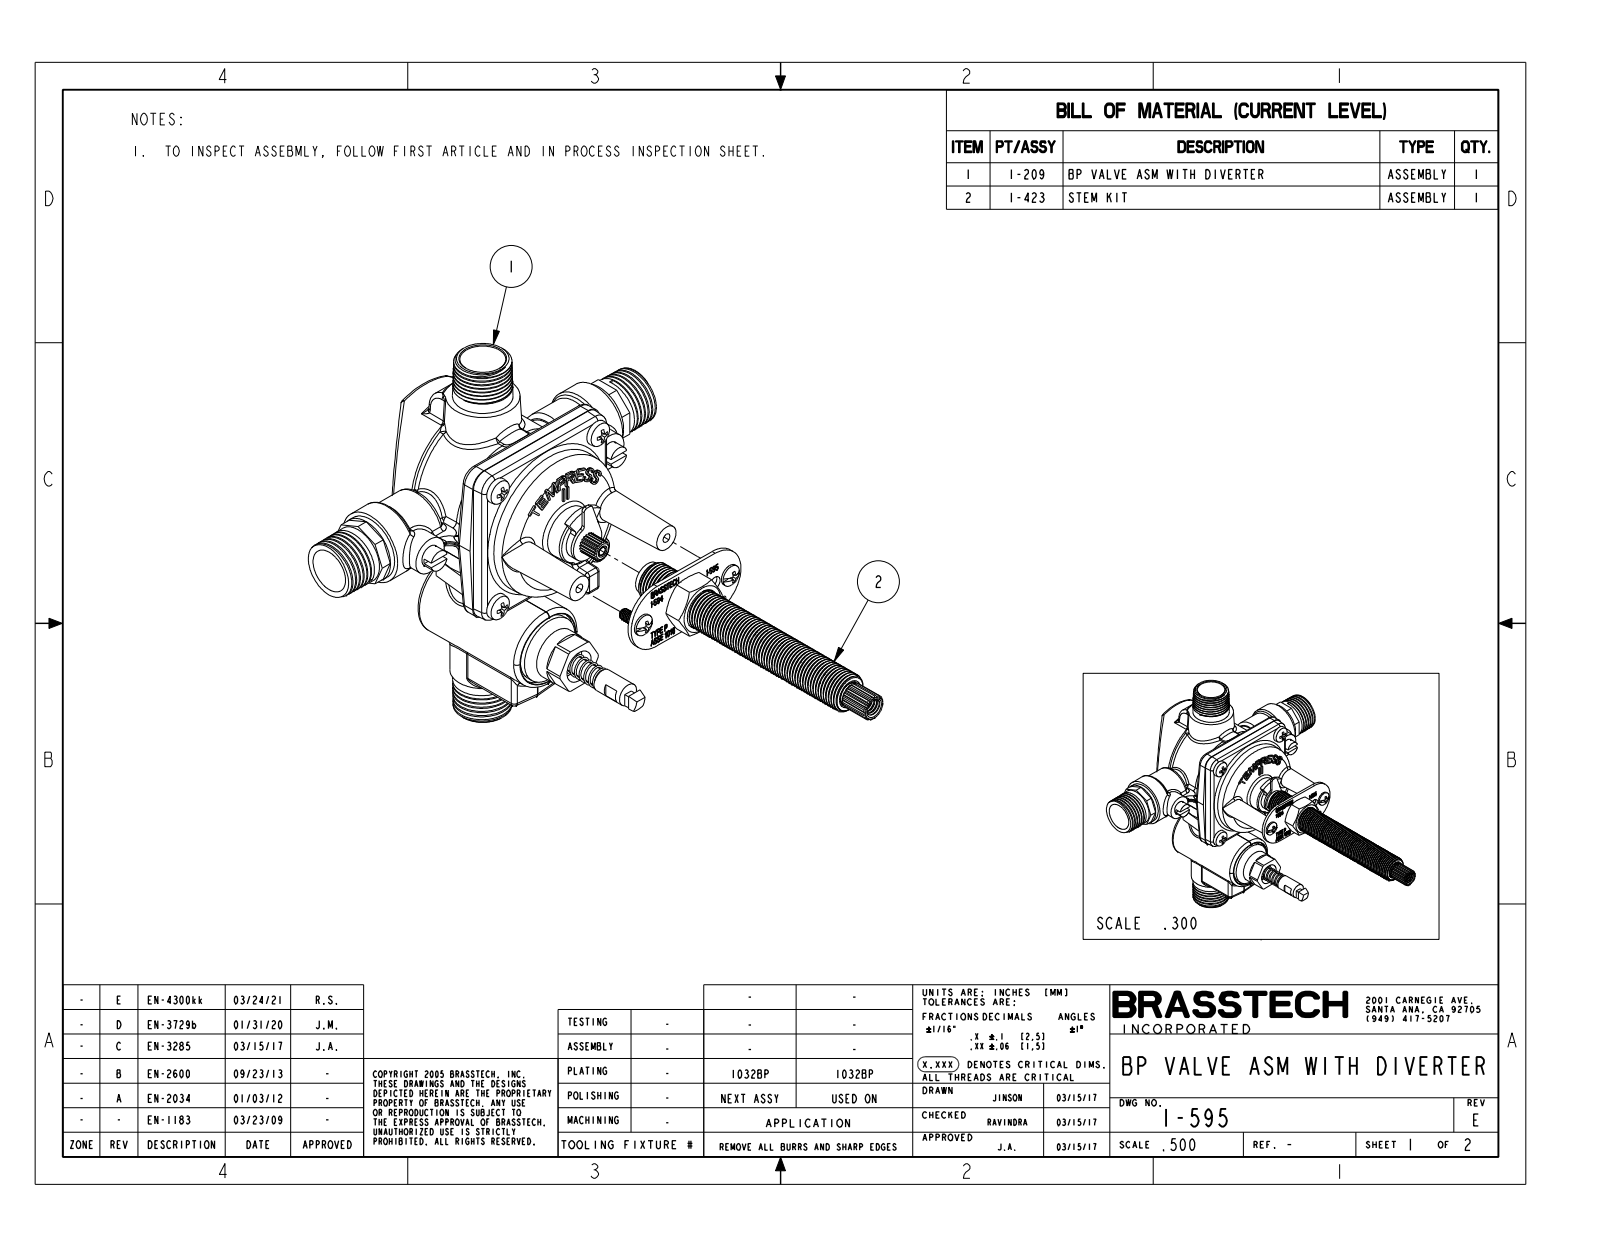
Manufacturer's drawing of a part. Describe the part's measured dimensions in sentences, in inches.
The part is named "DEFAULT-19951; DEFAULT-39795; DEFAULT-40417; DEFAULT-41269 (+8 more)". Its 3-D file was written by "CREO PARAMETRIC BY PTC INC, 2018400 (AUTOMOTIVE_DESIGN)". It is 22 solids with 3865 faces: 1442 planar, 1097 cylindrical and 1326 other. Overall it measures 7.655 by 5.961 by 5.866 inches. Its volume is 18.44 cubic inches and its surface area 148.8 square inches. Round holes: 4 of diameter 0.171, 4 of diameter 0.237, 3 of diameter 0.2, 2 of diameter 0.315, 2 of diameter 0.374, 2 of diameter 0.63, 1 of diameter 0.138, 1 of diameter 0.202, 1 of diameter 0.274, 1 of diameter 0.396, 1 of diameter 0.398, 1 of diameter 0.47. Round bosses or shafts: 4 of diameter 0.19, 2 of diameter 0.945, 2 of diameter 0.551, 2 of diameter 0.354, 2 of diameter 0.315, 2 of diameter 0.313, 2 of diameter 0.217, 2 of diameter 0.157. Partial cylindrical surfaces (rounded edges, fillets, slot ends): 74 of radius 0.063, 17 of radius 0.05, 10 of radius 0.039, 9 of radius 0.06, 6 of radius 0.063, 4 of radius 0.094, 4 of radius 0.217, 3 of radius 0.07. The main face-to-face distances are 0.13, 0.118, 1.65, 1.78, 0.315, 0.185, 1.877, 1.125, 3.465, 1.815. The hole center spacings are 1.241, 1.375, 1.945, 2.885, 0.845, 0.899, 0.976, 0.986.
